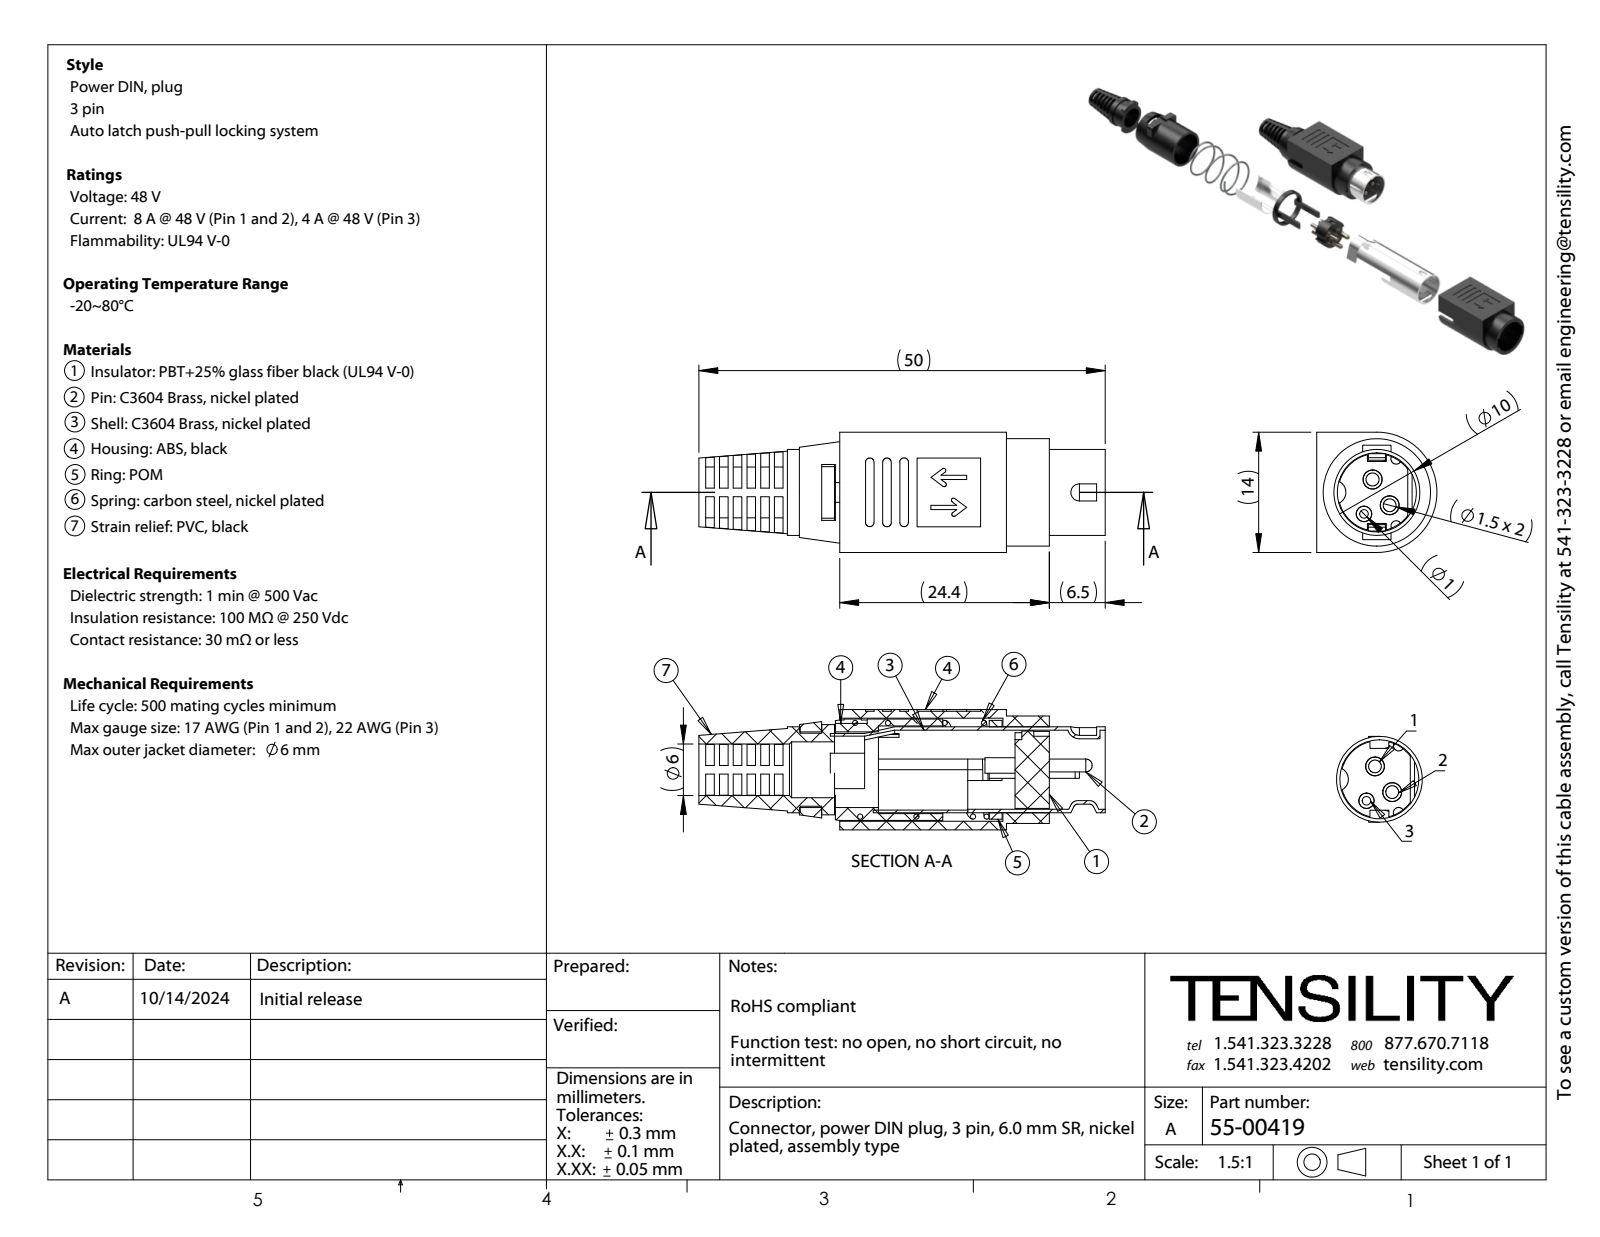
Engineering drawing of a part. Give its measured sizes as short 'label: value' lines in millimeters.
name: 55-00419-06_默认; 55-00419-02_默认; 55-00419-01_默认; 55-00419-08_默认 (+7 more)
written by: SolidWorks 2025 (CONFIG_CONTROL_DESIGN)
unit: mm
bodies: 11 solids, 403 faces (266 planar, 111 cylindrical, 26 other)
size: 47.3 × 14 × 14
volume: 2 706 mm³; area: 7 477 mm²
holes: 2× ⌀1.2, 1× ⌀0.7, 1× ⌀6, 1× ⌀6.5, 1× ⌀8.8, 1× ⌀9.2, 1× ⌀10.2
bosses: 3× ⌀1.8, 2× ⌀2.2, 2× ⌀1.5, 1× ⌀12.5, 1× ⌀11.8, 1× ⌀11.5, 1× ⌀10, 1× ⌀9
rounds: 8× R0.5, 4× R1, 3× R0.6, 2× R0.25, 2× R0.25, 2× R0.9, 1× R1.4, 1× R1.5
face distances: 1, 1.6, 13, 1.5, 0.5, 0.6, 12, 5, 5.5, 7
hole spacings: 1.58, 2.12, 2.92, 3.16, 3.61, 4.12
